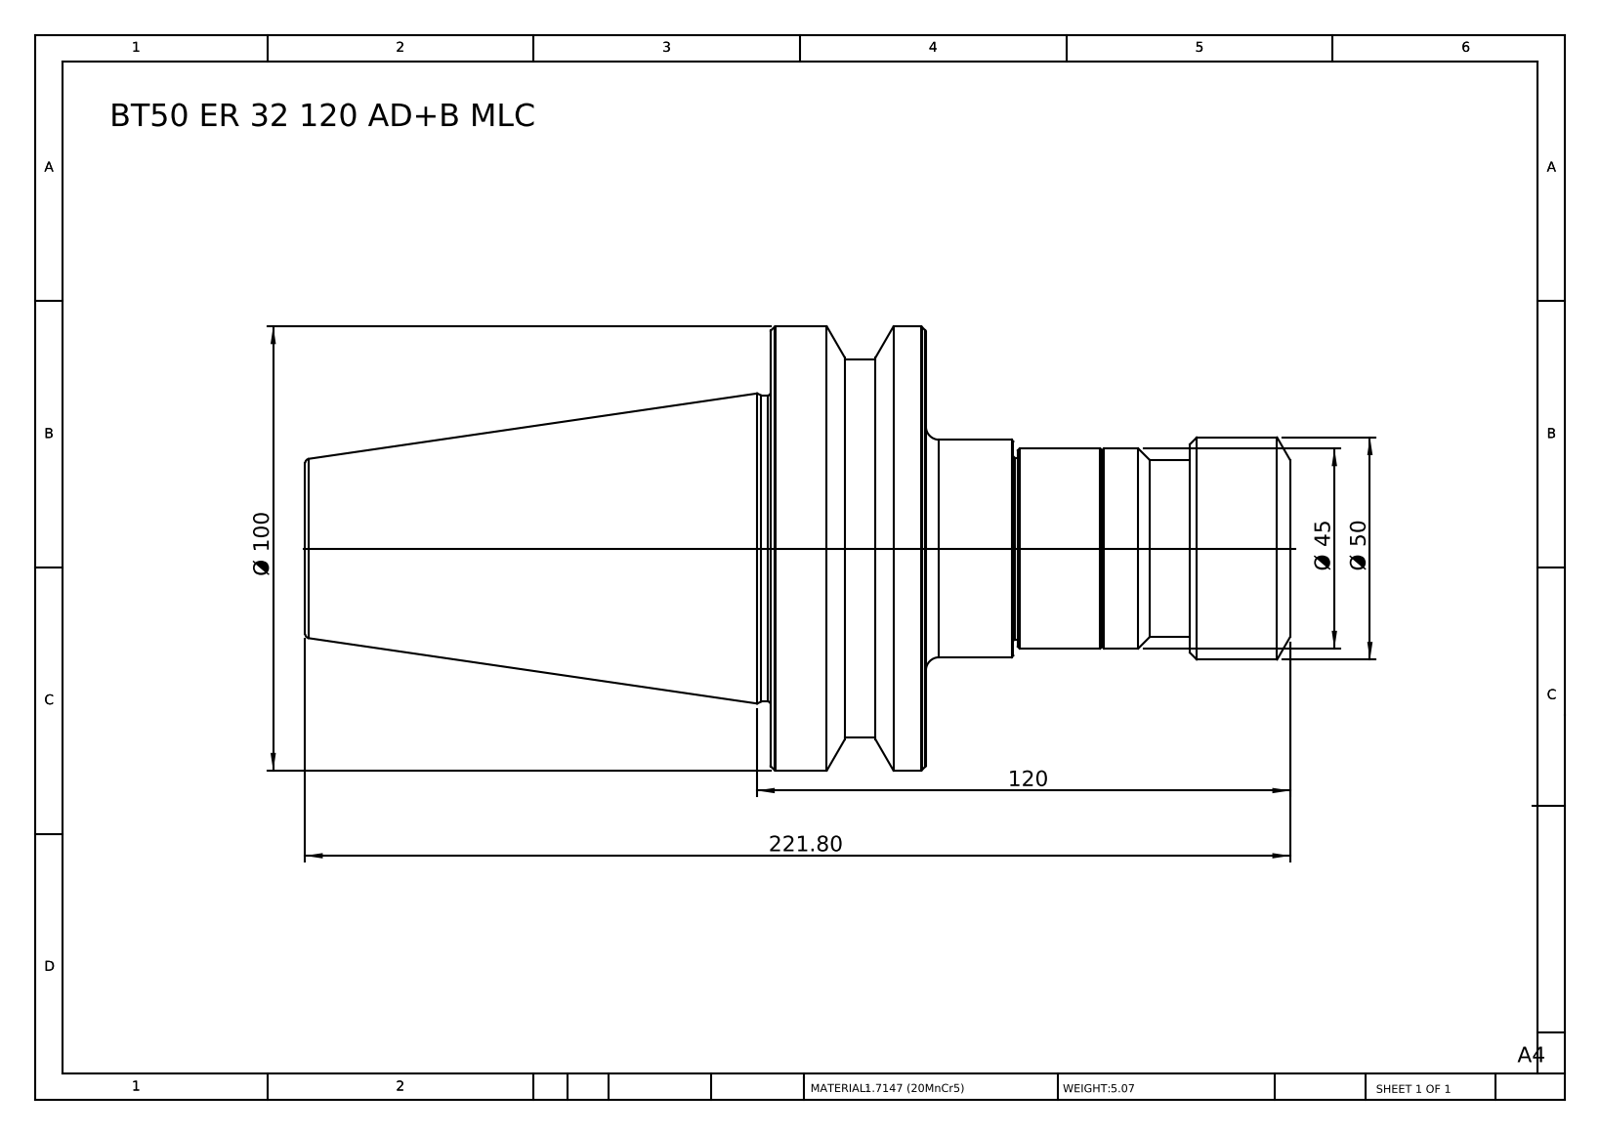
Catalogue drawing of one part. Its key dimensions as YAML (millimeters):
part_name: "BT50 ER 32 120 AD+B MLC"
step_written_by: "SolidWorks 2014 (CONFIG_CONTROL_DESIGN)"
units: millimeters
bodies: {solids: 1, faces: 71, planar: 9, cylindrical: 20, other: 42}
overall_size: [221.8, 100, 100]
volume: 649881
surface_area: 57415
round_bosses_or_shafts:
  - {diameter: 100, count: 1}
  - {diameter: 85, count: 1}
  - {diameter: 69, count: 1}
  - {diameter: 50, count: 1}
  - {diameter: 49, count: 1}
  - {diameter: 45, count: 1}
  - {diameter: 40.9, count: 1}
  - {diameter: 39.9, count: 1}
face_to_face_distances: [35, 82, 117, 221.8, 139.8, 104.8, 22.5, 59.5, 94.5, 199.3]
